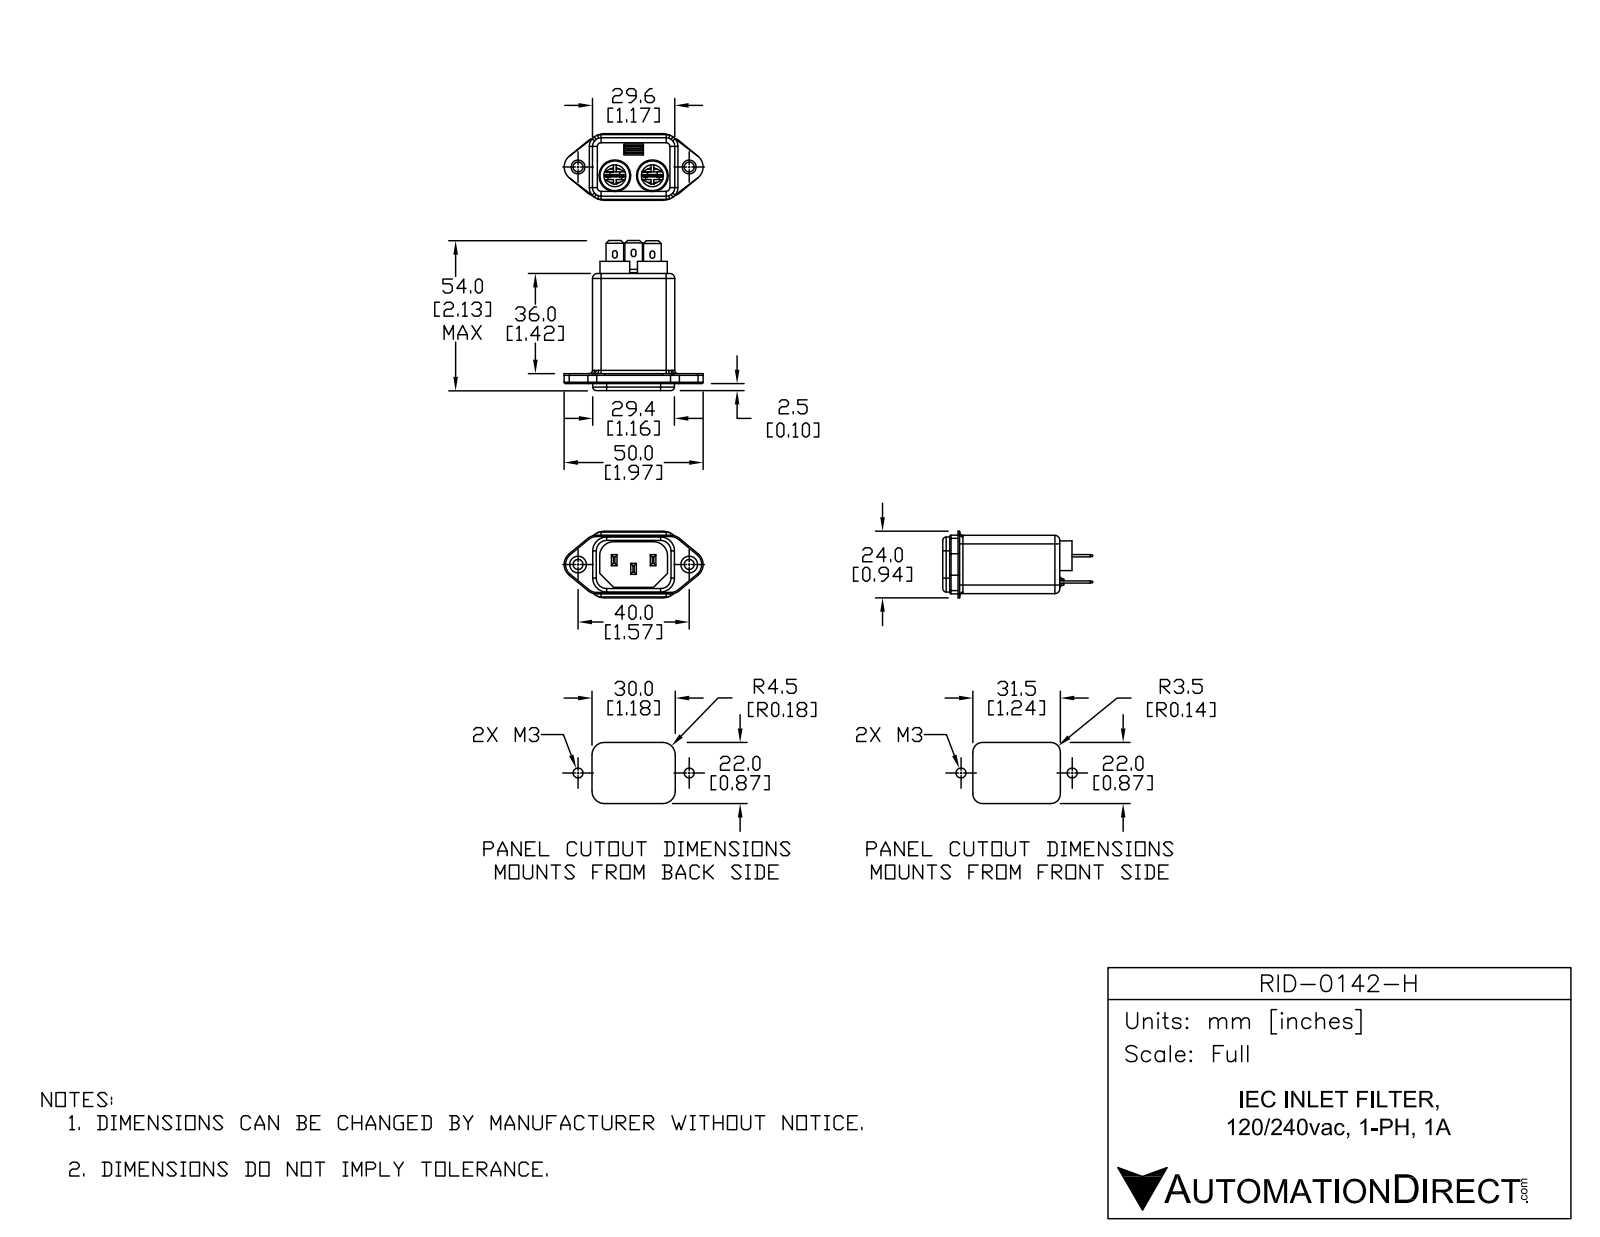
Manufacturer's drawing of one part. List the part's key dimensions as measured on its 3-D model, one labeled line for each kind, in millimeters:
Part name (STEP PRODUCT): inlet body DAC-3; ENCLOSURE A1_+; RID0142H
STEP written by: SolidWorks 2015 (AUTOMOTIVE_DESIGN)
Units: millimetres
Bodies: 11 solids, 591 faces (410 planar, 142 cylindrical, 39 other)
Overall size (bounding box): 54 × 50 × 24
Volume: 12 008 mm³ · Surface area: 20 049 mm²
Round holes (diameter × count): ⌀1.5 ×2, ⌀1.65 ×2, ⌀3.6 ×2, ⌀5 ×2, ⌀7.9 ×2, ⌀11.4 ×2, ⌀1.75 ×1
Round bosses / shafts (diameter × count): ⌀10.7 ×2
Partial cylindrical surfaces — rounded edges, fillets, slot ends (radius × count): R5 ×12, R0.3 ×11, R0.5 ×8, R1 ×8, R0.8 ×7, R1.25 ×6, R2.5 ×6, R1.75 ×4
Main face-to-face distances: 0.6, 20.4, 21, 19.8, 29, 1.05, 28.9, 36, 1.45, 11.2
Hole centre spacings: 13.5, 13.62, 26.93, 6.77, 6.78, 10.47, 10.77, 11.21
